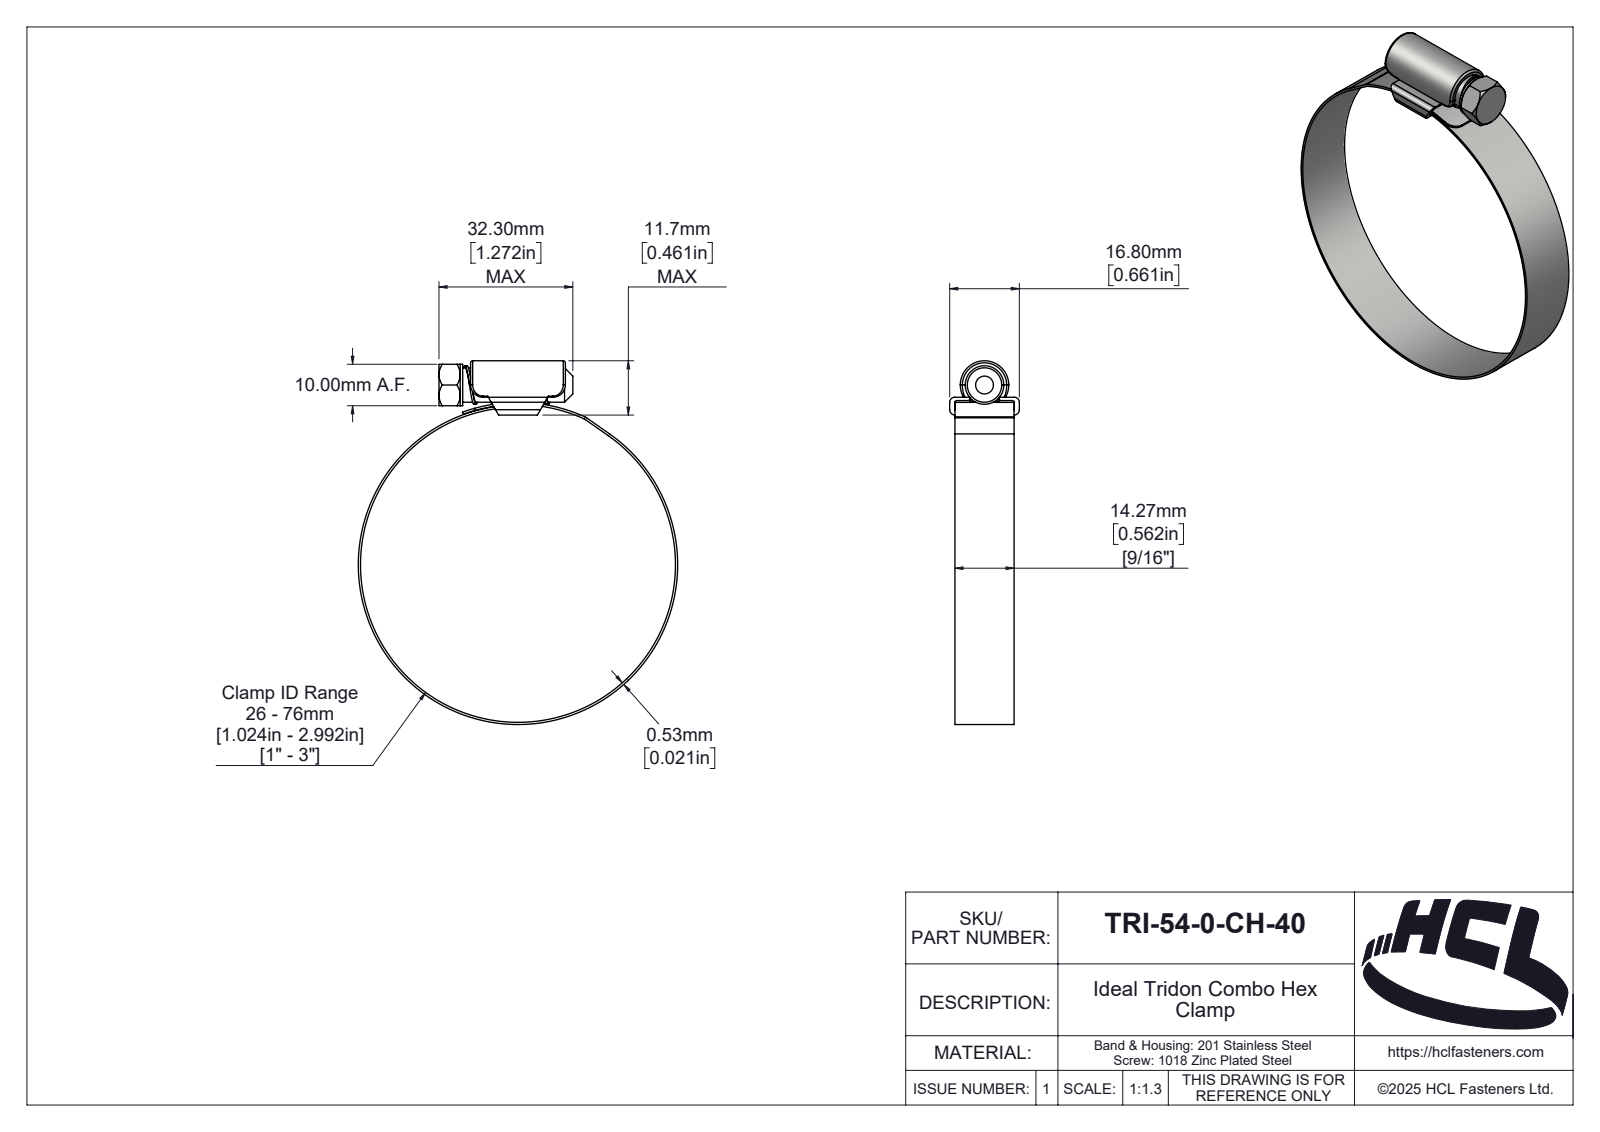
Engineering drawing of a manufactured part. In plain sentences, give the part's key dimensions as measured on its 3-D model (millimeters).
The part is named "TRI-54-0-CH-40". Its 3-D file was written by "SolidWorks 2025 (AUTOMOTIVE_DESIGN)". It is 3 solids with 212 faces: 35 planar, 101 cylindrical and 76 other. Overall it measures 87.73 by 77.06 by 16.8 millimeters. Its volume is 4 808 cubic millimeters and its surface area 10 512 square millimeters. Round holes: 1 of diameter 76. Round bosses or shafts: 1 of diameter 77.06, 1 of diameter 10, 1 of diameter 8.3. Partial cylindrical surfaces (rounded edges, fillets, slot ends): 6 of radius 0.5, 4 of radius 3, 2 of radius 0.1, 2 of radius 1.2, 2 of radius 1.3, 1 of radius 0.46, 1 of radius 1.89, 1 of radius 2. The main face-to-face distances are 1.2, 14.26, 0.53, 3.5, 2.3, 4.3, 3.1, 0.8, 9.99, 1.27.
